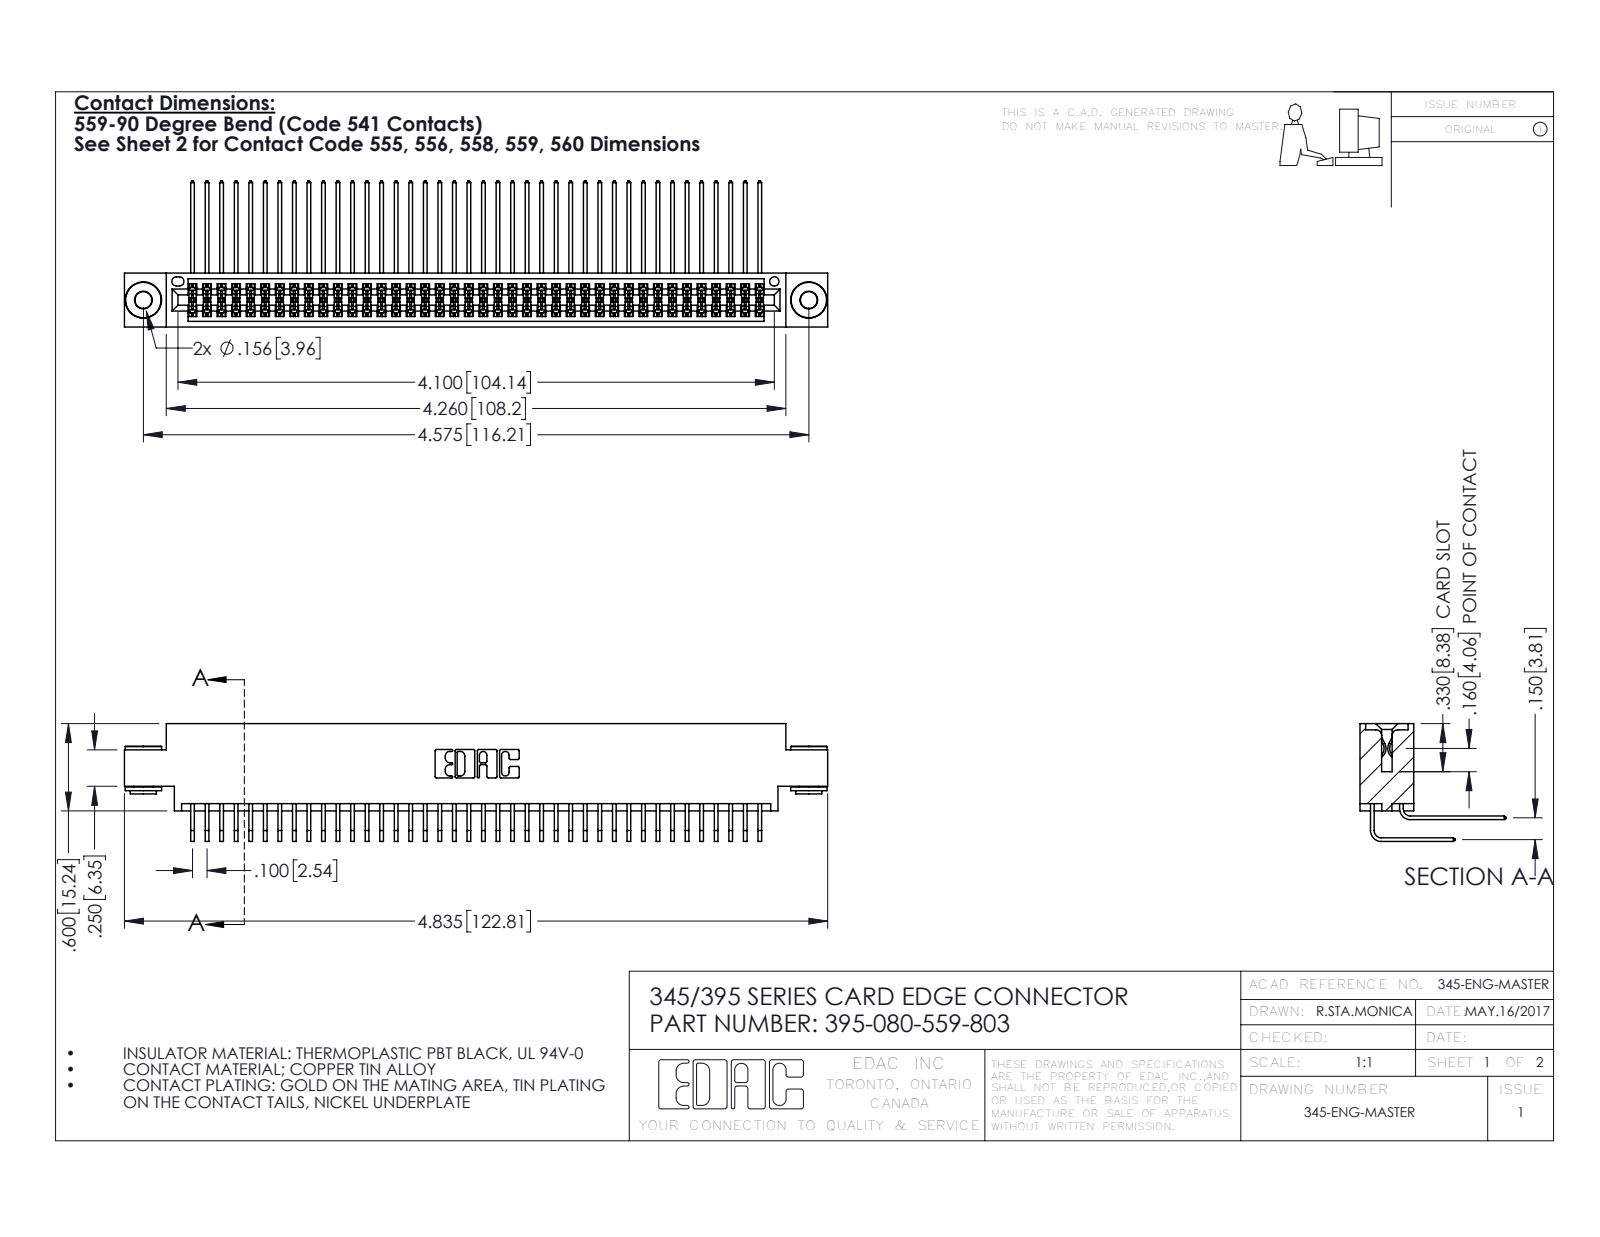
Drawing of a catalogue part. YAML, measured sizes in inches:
part_name: "345-292-001_559 Tail - 2; 345-250-002_345-250-002-102; 345-292-001_558 559 Tail - 1; 395-080-559-803 (+1 more)"
step_written_by: "SolidWorks 2016 (CONFIG_CONTROL_DESIGN)"
units: inches
bodies: {solids: 83, faces: 4328, planar: 2894, cylindrical: 1426, other: 8}
overall_size: [4.835, 1.005, 0.809]
volume: 0.749
surface_area: 31.98
round_holes:
  - {diameter: 0.116, count: 2}
  - {diameter: 0.156, count: 2}
  - {diameter: 0.064, count: 1}
round_bosses_or_shafts:
  - {diameter: 0.25, count: 2}
  - {diameter: 0.18, count: 2}
  - {diameter: 0.136, count: 2}
partial_cylinders:
  - {radius: 0.006, count: 121}
  - {radius: 0.01, count: 22}
  - {radius: 0.007, count: 6}
  - {radius: 0.031, count: 6}
  - {radius: 0.026, count: 3}
  - {radius: 0.014, count: 2}
  - {radius: 0.019, count: 2}
  - {radius: 0.022, count: 2}
face_to_face_distances: [0.072, 0.298, 0.37, 0.2, 0.098, 0.272, 0.025, 0.175, 0.225, 0.15]
hole_center_spacings: [0.27, 4.339, 4.575]
